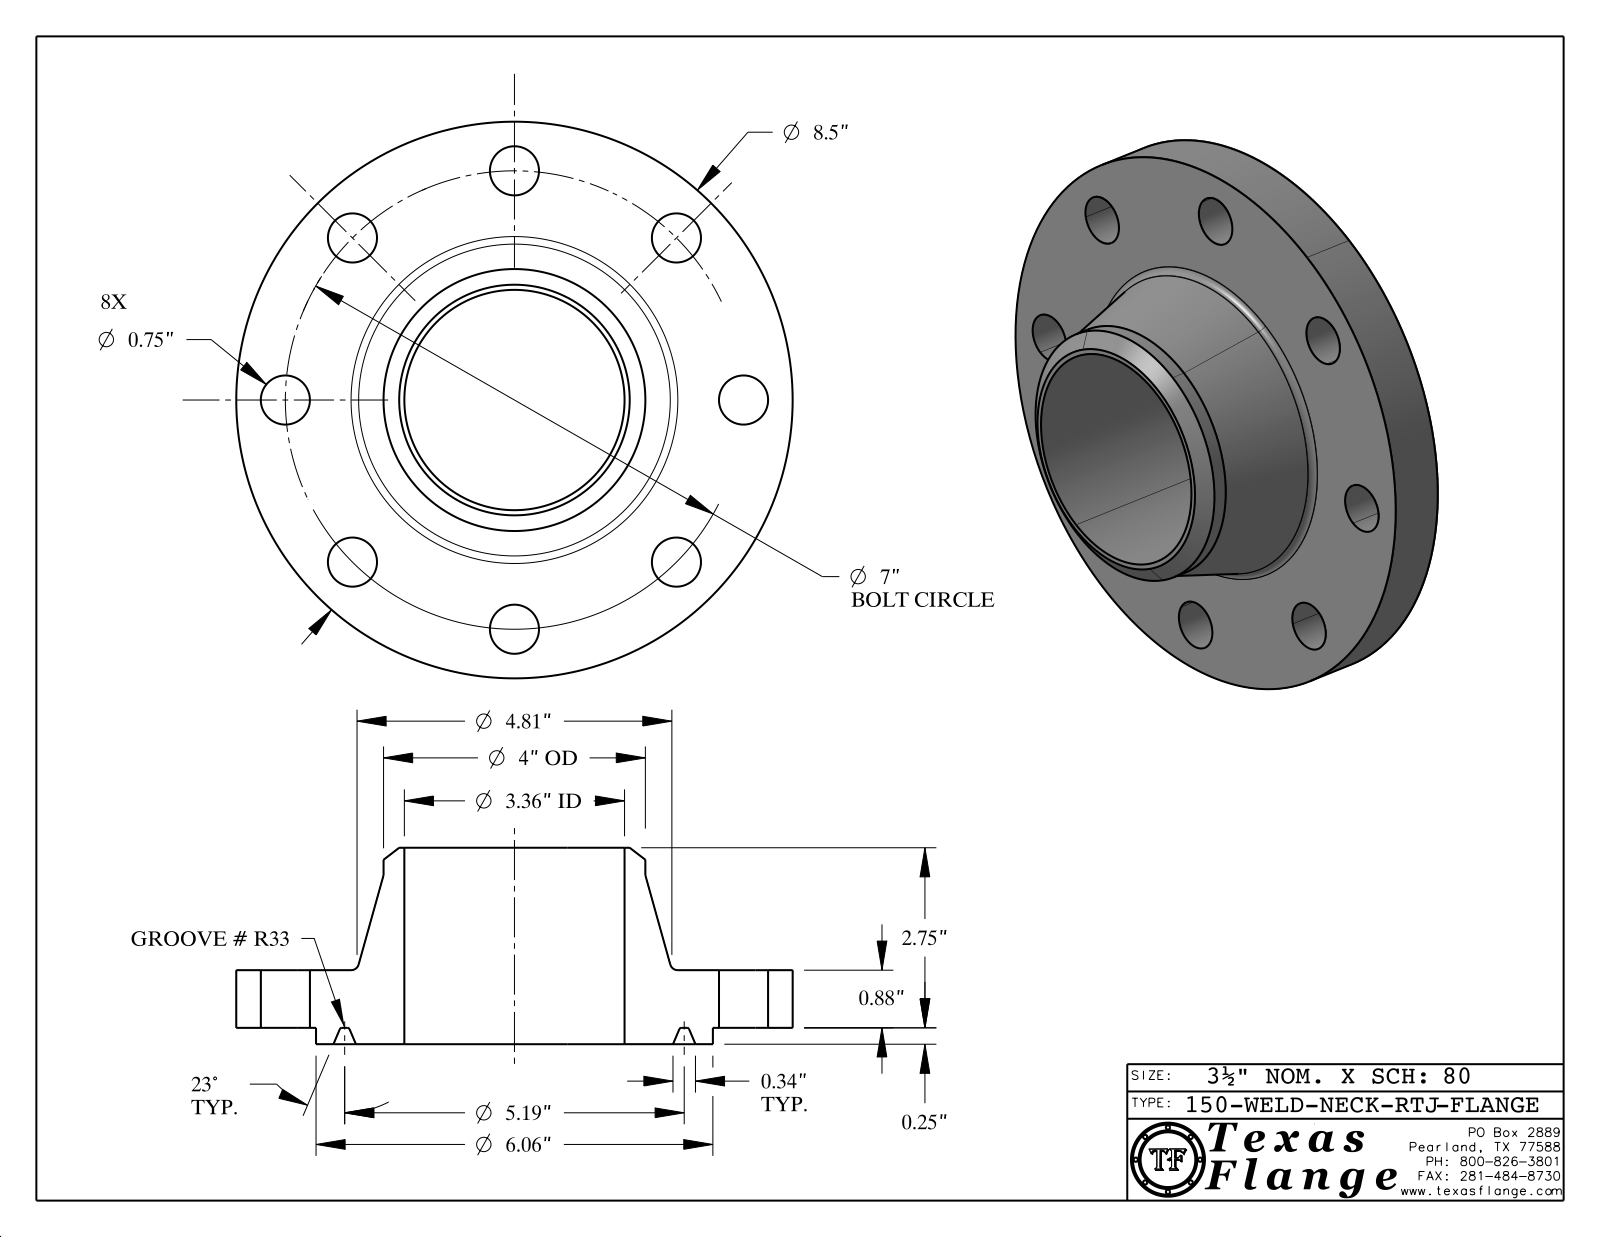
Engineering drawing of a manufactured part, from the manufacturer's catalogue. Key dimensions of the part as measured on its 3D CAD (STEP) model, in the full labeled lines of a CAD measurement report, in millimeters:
Part name (STEP PRODUCT): 150-WELD-NECK-RTJ
STEP written by: CATIA V5 STEP AP214 (AUTOMOTIVE_DESIGN)
Units: millimetres
Bodies: 1 solid, 429 faces (371 planar, 44 cylindrical, 14 other)
Overall size (bounding box): 215.9 × 215.9 × 76.2
Volume: 878 500 mm³ · Surface area: 121 900 mm²
Round holes (diameter × count): ⌀19.1 ×8, ⌀12.6 ×1, ⌀85.4 ×1
Round bosses / shafts (diameter × count): ⌀0.8 ×8, ⌀215.9 ×1, ⌀154 ×1, ⌀101.6 ×1, ⌀9.9 ×1
Main face-to-face distances: 22.4, 6.4, 28.7, 76.2, 69.9, 47.5, 28.6, 22.2, 47.6, 3.8
Hole centre spacings: 88.9, 68, 125.7, 164.3, 34.7, 98.8, 147.8, 174.4
